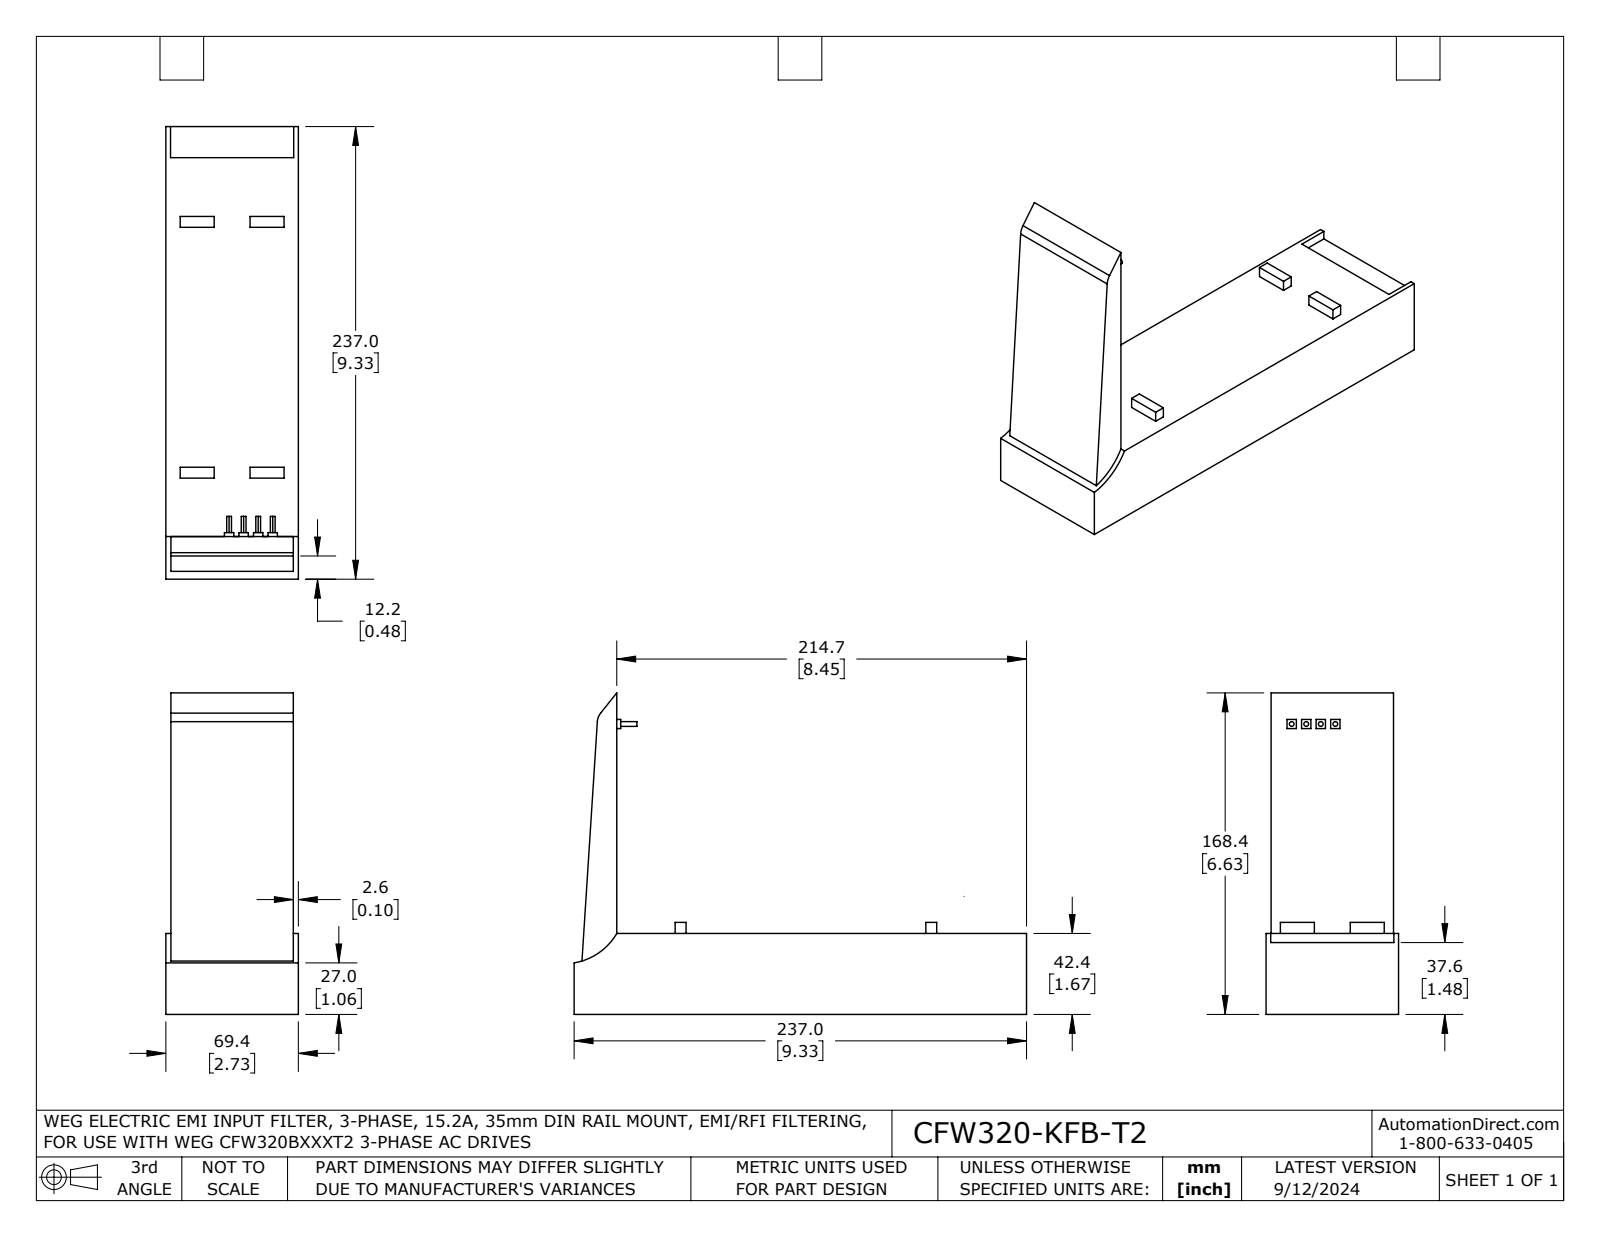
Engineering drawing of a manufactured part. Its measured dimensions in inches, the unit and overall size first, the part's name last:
Units: inches
Overall size (bounding box): 9.331 × 6.628 × 2.732
Round bosses / shafts (diameter × count): ⌀0.098 ×4
Partial cylindrical surfaces — rounded edges, fillets, slot ends (radius × count): R0.315 ×1, R1.26 ×1
Main face-to-face distances: 1.669, 2.733, 8.452, 9.331, 0.879, 0.104, 2.628, 2.629, 2.524, 0.104
Volume: 48.38 in³ · Surface area: 122.1 in²
Bodies: 1 solid, 69 faces (59 planar, 10 cylindrical, 0 other)
Part name (STEP PRODUCT): CFW320-KFB-T2
STEP written by: SolidWorks 2021 (AUTOMOTIVE_DESIGN)
